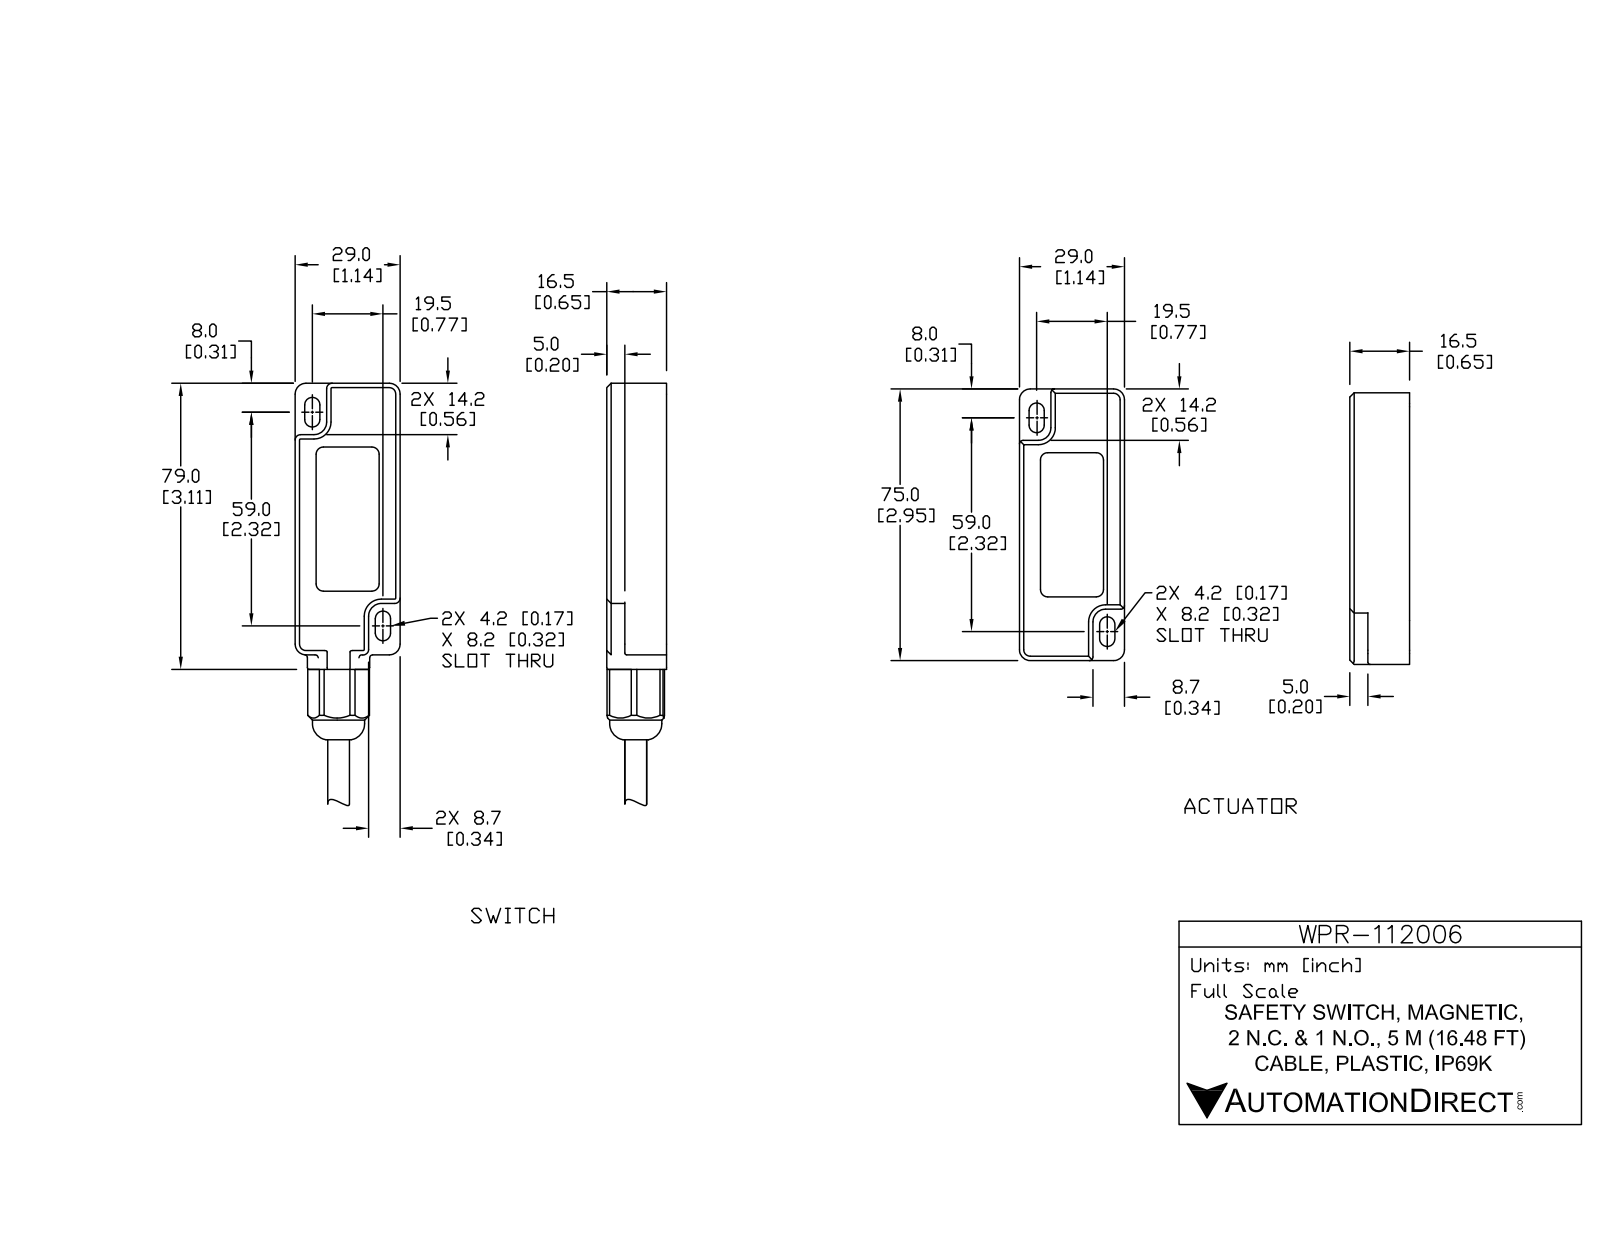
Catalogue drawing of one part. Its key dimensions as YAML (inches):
part_name: "WPR-112006_1; WPR-112006; WPR-112006_2"
step_written_by: "SolidWorks 2017 (AUTOMOTIVE_DESIGN)"
units: inches
bodies: {solids: 11, faces: 1294, planar: 573, cylindrical: 348, other: 373}
overall_size: [12.953, 2.323, 0.65]
volume: 2.63
surface_area: 65.38
round_holes:
  - {diameter: 0.195, count: 4}
  - {diameter: 0.276, count: 1}
  - {diameter: 0.327, count: 1}
  - {diameter: 0.465, count: 1}
  - {diameter: 0.472, count: 1}
round_bosses_or_shafts:
  - {diameter: 0.031, count: 8}
  - {diameter: 0.193, count: 4}
  - {diameter: 0.079, count: 4}
  - {diameter: 0.091, count: 2}
  - {diameter: 0.567, count: 1}
  - {diameter: 0.531, count: 1}
  - {diameter: 0.469, count: 1}
  - {diameter: 0.461, count: 1}
partial_cylinders:
  - {radius: 0.02, count: 85}
  - {radius: 0.039, count: 20}
  - {radius: 0.008, count: 10}
  - {radius: 0.047, count: 8}
  - {radius: 0.079, count: 8}
  - {radius: 0.083, count: 8}
  - {radius: 0.118, count: 8}
  - {radius: 0.024, count: 4}
face_to_face_distances: [0.071, 0.575, 1.181, 1.071, 0.646, 0.067, 0.571, 0.075, 0.504, 0.579]
hole_center_spacings: [2.047, 0.9, 1.459, 2.344, 2.347]
